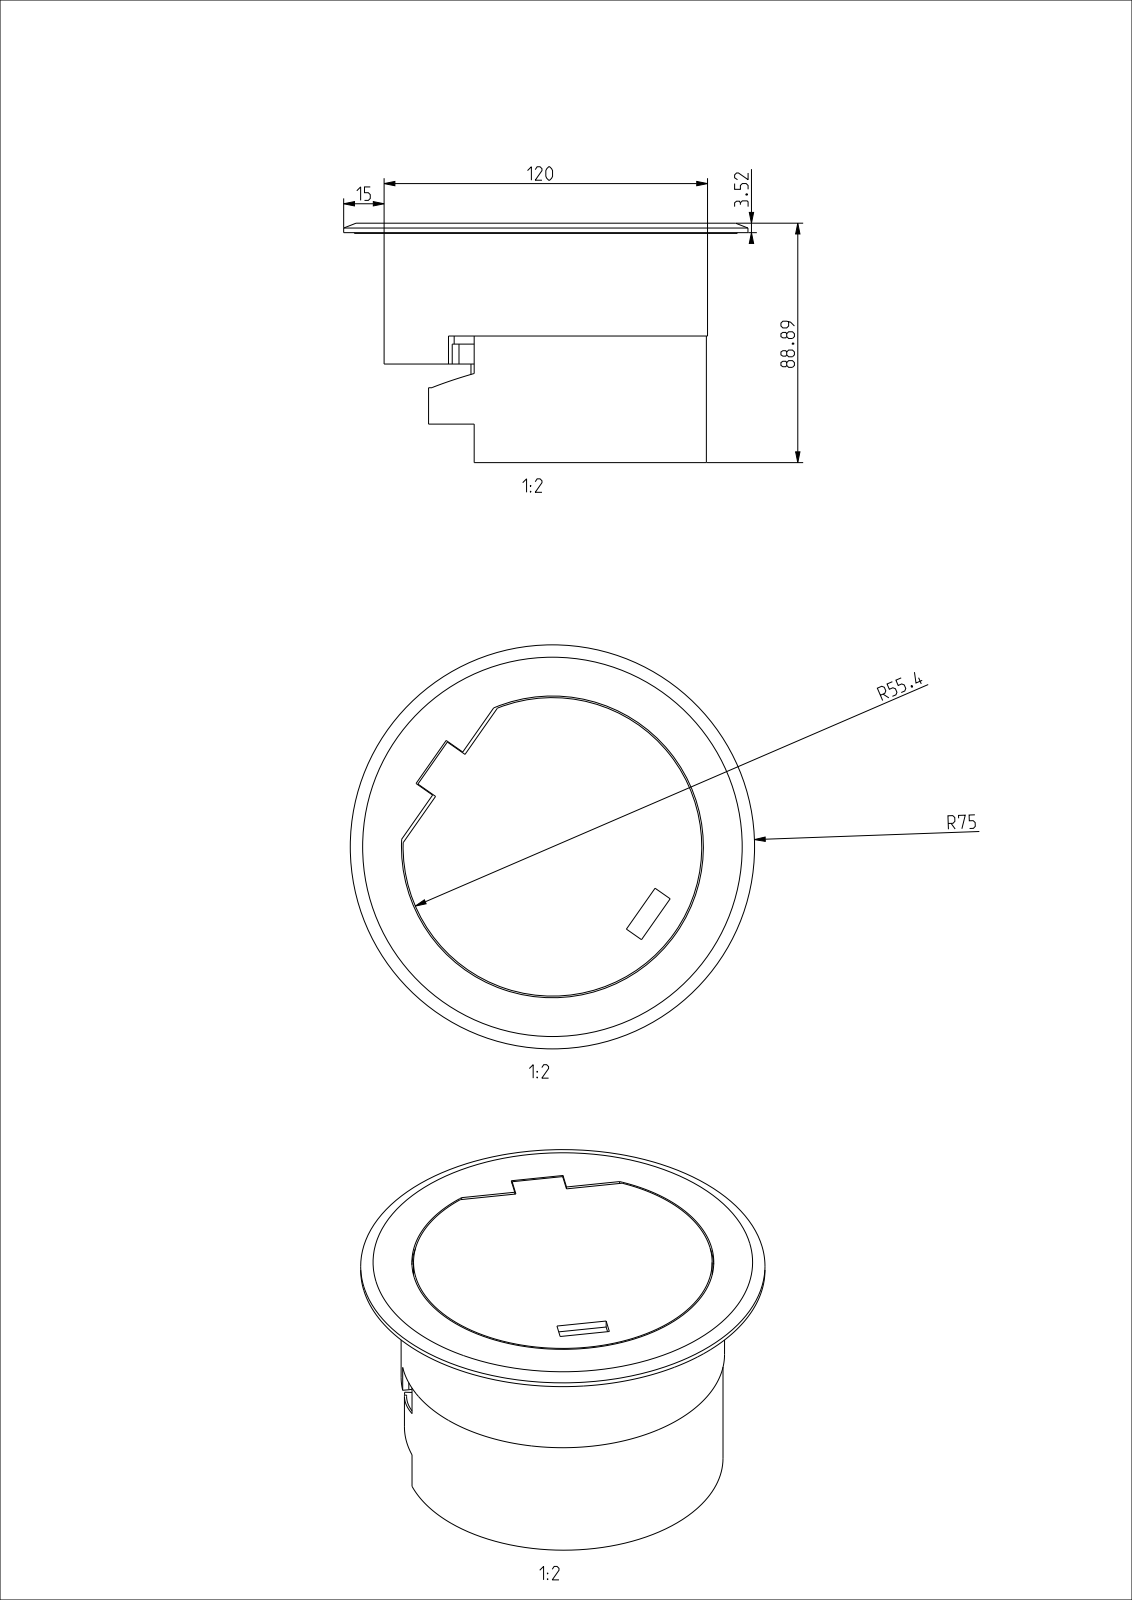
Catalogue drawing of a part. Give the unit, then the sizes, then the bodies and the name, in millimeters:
Units: millimetres
Overall size (bounding box): 150 × 150 × 88.89
Round holes (diameter × count): ⌀5.7 ×4, ⌀2.73 ×2, ⌀38.3 ×2, ⌀2 ×1, ⌀3.6 ×1, ⌀115.4 ×1, ⌀146.19 ×1
Round bosses / shafts (diameter × count): ⌀4.69 ×2, ⌀150 ×1, ⌀142 ×1, ⌀120 ×1, ⌀116.81 ×1, ⌀112 ×1, ⌀110.8 ×1
Partial cylindrical surfaces — rounded edges, fillets, slot ends (radius × count): R50 ×2, R52 ×2, R51 ×1, R53 ×1, R54.45 ×1, R55 ×1, R56.5 ×1, R56.59 ×1
Main face-to-face distances: 1.5, 36.6, 38.1, 88.89, 79.59, 9.3, 78.09, 87.39, 41.49, 50.79
Hole centre spacings: 8.85, 45, 17.68, 43.12, 15.83, 21.17, 22.93, 24.23
Volume: 377 634 mm³ · Surface area: 212 219 mm²
Bodies: 6 solids, 350 faces (285 planar, 61 cylindrical, 4 other)
Part name (STEP PRODUCT): BSR_BECHERUNTERTEIL; BSR_BECHEROBERTEIL; BSR_GERTEAUFNAHME0; BSM012KUN (+3 more)
STEP written by: CREO PARAMETRIC BY PTC INC, 2022024 (AUTOMOTIVE_DESIGN)
